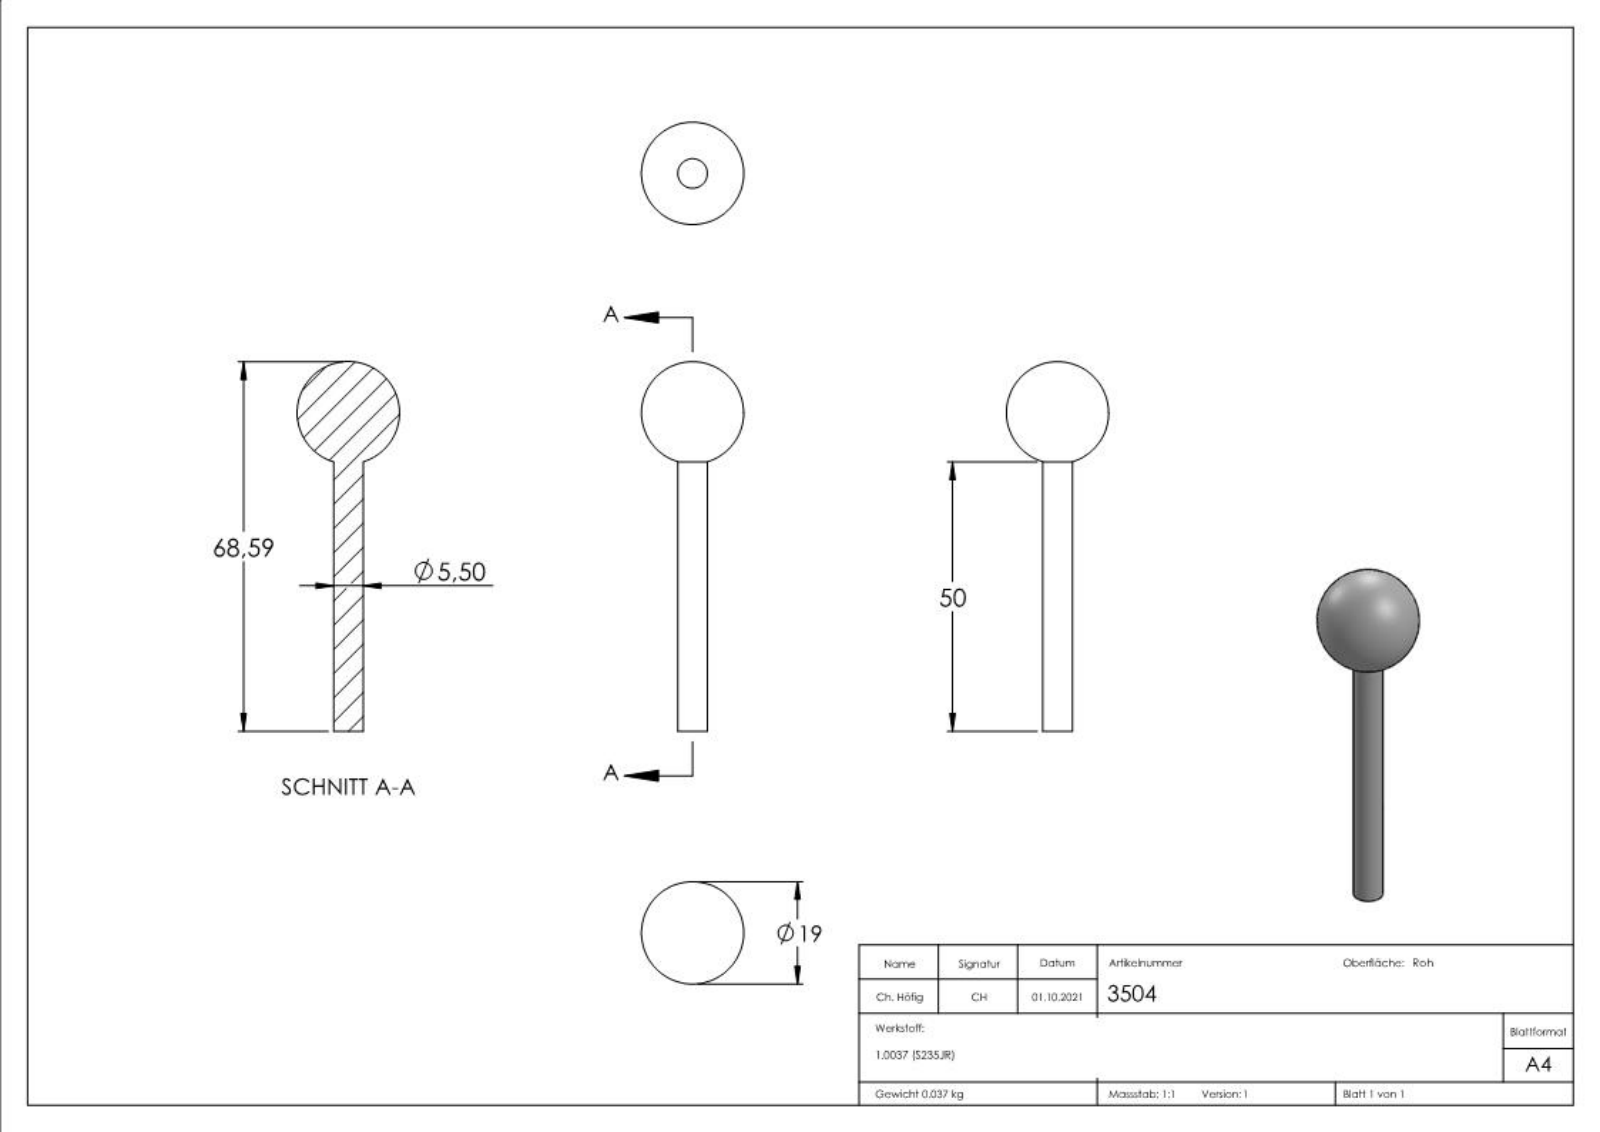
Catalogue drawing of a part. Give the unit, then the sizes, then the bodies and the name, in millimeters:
Units: millimetres
Overall size (bounding box): 68.59 × 19 × 19
Round bosses / shafts (diameter × count): ⌀5.5 ×1
Volume: 4 774 mm³ · Surface area: 1 998 mm²
Bodies: 1 solid, 5 faces (1 planar, 2 cylindrical, 2 other)
Part name (STEP PRODUCT): 3504
STEP written by: SolidWorks 2015 (CONFIG_CONTROL_DESIGN)
